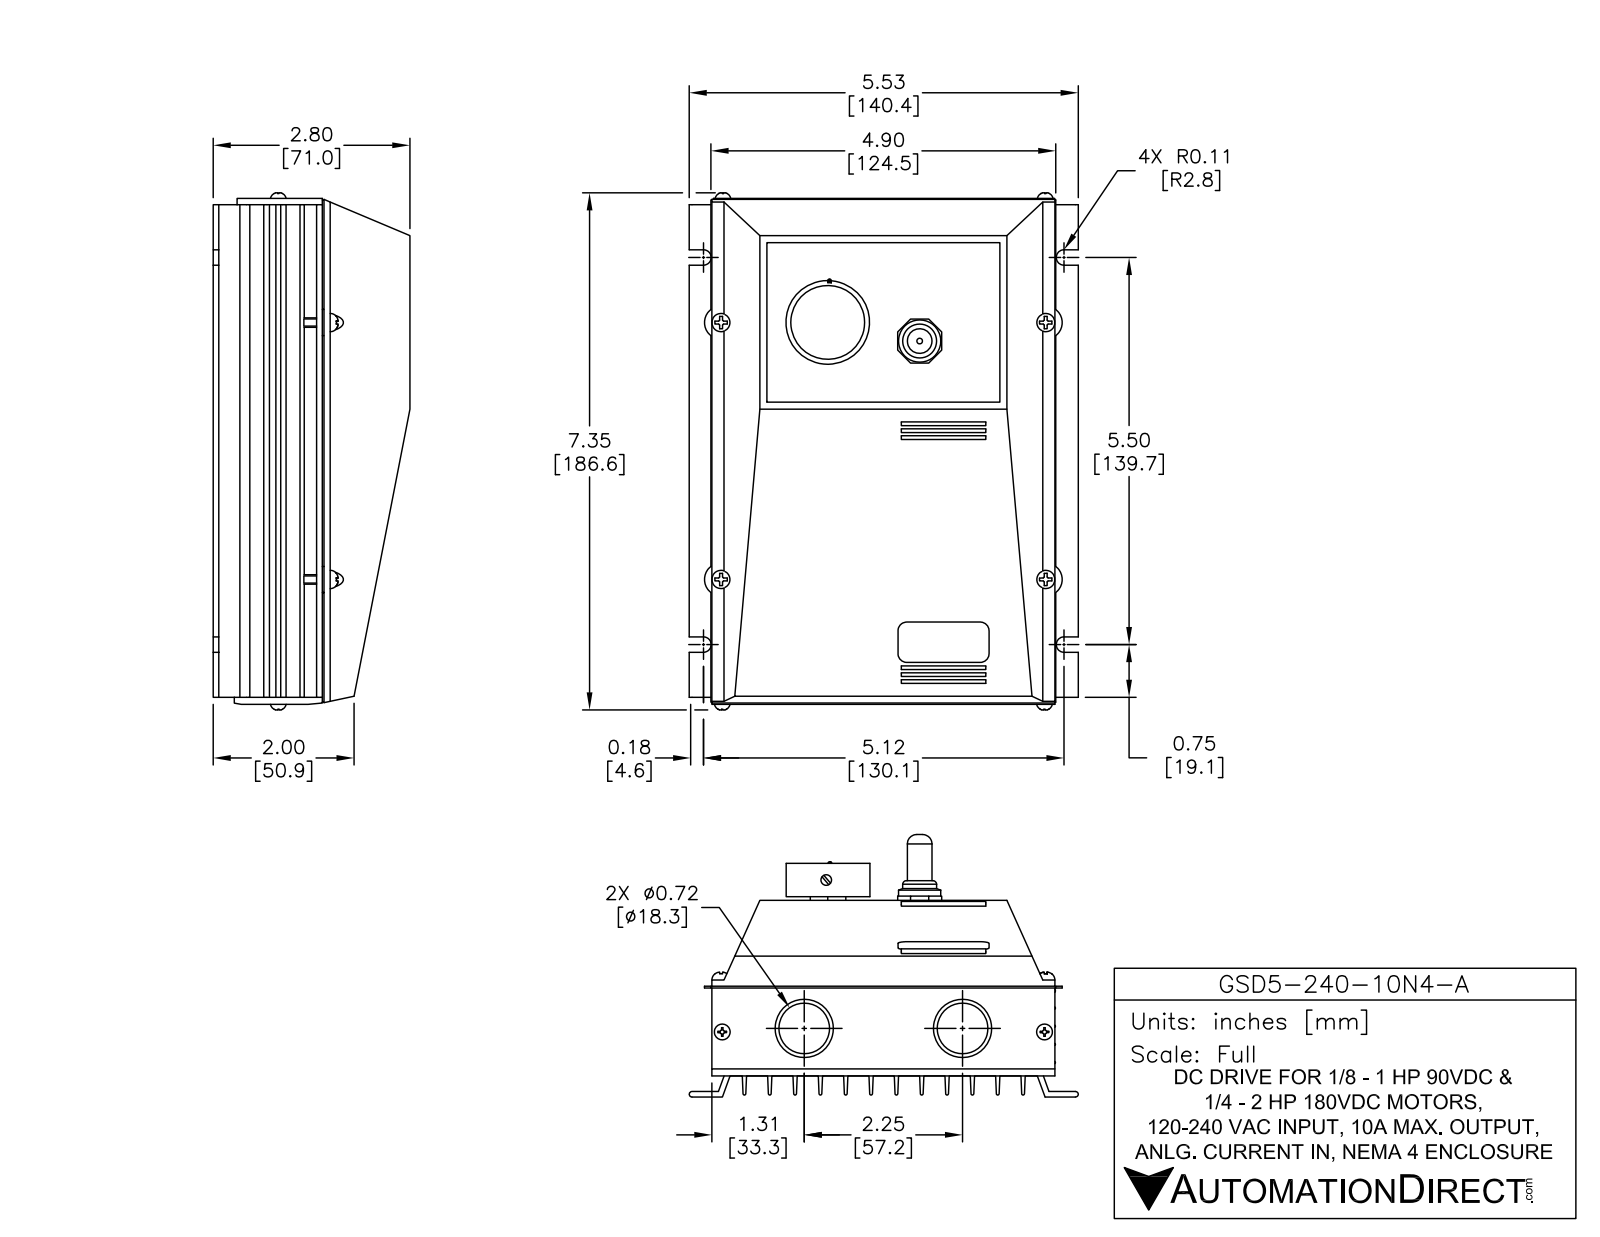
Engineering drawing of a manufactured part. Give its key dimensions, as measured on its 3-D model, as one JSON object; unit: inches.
{"part_name": "Nut-Switch_Basic-0.5575W-.4625Dia; HDS6P10_#6_.375_TypeB PhilHd Blk Oxide; Speedpot_Knob; PC250G (+8 more)", "step_written_by": "SolidWorks 2014 (AUTOMOTIVE_DESIGN)", "units": "inches", "bodies": {"solids": 26, "faces": 2622, "planar": 1879, "cylindrical": 624, "other": 119}, "overall_size": [7.346, 5.529, 3.589], "volume_in3": 19.61, "surface_area_in2": 471.5, "round_holes": [[0.14, 11], [0.276, 5], [0.113, 4], [0.075, 3], [0.095, 3], [0.104, 3], [0.719, 2], [1.32, 2], [0.059, 1], [0.15, 1], [0.375, 1], [0.38, 1]], "round_bosses_or_shafts": [[0.237, 11], [0.14, 11], [0.065, 7], [0.173, 5], [0.134, 4], [0.13, 4], [0.112, 4], [0.065, 4]], "partial_cylinders_radius": [[0.025, 92], [0.02, 19], [0.05, 16], [0.39, 11], [0.486, 11], [0.02, 8], [0.125, 8], [0.03, 6]], "face_to_face_distances": [0.1, 0.719, 0.08, 1.439, 2.371, 0.358, 0.458, 2.158, 0.396, 0.296], "hole_center_spacings": [3.65, 4.604, 4.614, 4.615, 5.875, 5.883, 0.831, 2.496]}
